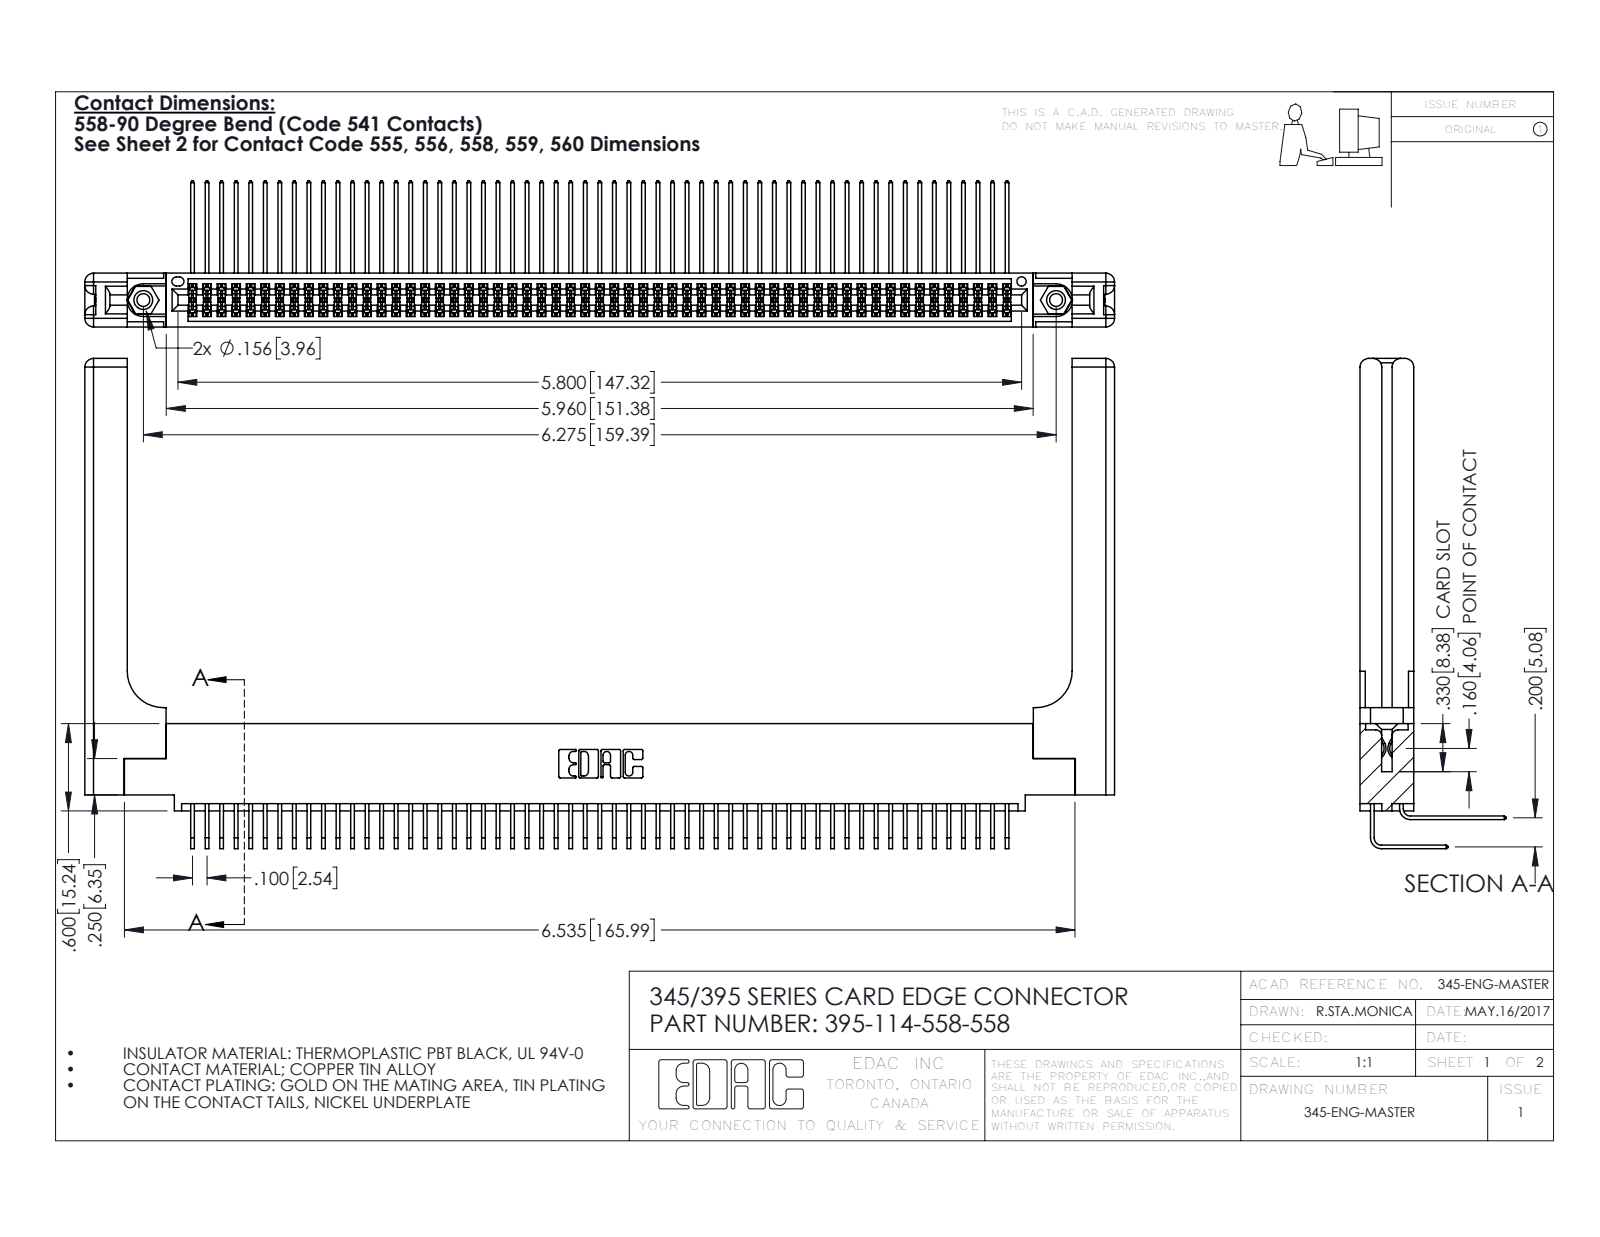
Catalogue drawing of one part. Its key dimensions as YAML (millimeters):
part_name: "345-292-001_558 559 Tail - 1; 345-292-001_558 Tail - 2; 345-220-058_345-220-058; 345 Part_0.110 Offset - 0.156 Dia-TH (+2 more)"
step_written_by: "SolidWorks 2016 (CONFIG_CONTROL_DESIGN)"
units: millimeters
bodies: {solids: 119, faces: 6314, planar: 4222, cylindrical: 2032, other: 60}
overall_size: [179.8, 85.6, 25.5]
volume: 26660
surface_area: 35430
round_holes:
  - {diameter: 2.3, count: 2}
  - {diameter: 3.2, count: 2}
  - {diameter: 4, count: 2}
  - {diameter: 1.6, count: 1}
round_bosses_or_shafts:
  - {diameter: 3.9, count: 2}
partial_cylinders:
  - {radius: 0.2, count: 172}
  - {radius: 0.3, count: 22}
  - {radius: 1.5, count: 16}
  - {radius: 0.2, count: 6}
  - {radius: 0.8, count: 6}
  - {radius: 0.7, count: 3}
  - {radius: 0.4, count: 2}
  - {radius: 0.5, count: 2}
face_to_face_distances: [1.8, 7.6, 9.4, 5.1, 2.5, 6.9, 0.6, 5.7, 3.8, 3.8]
hole_center_spacings: [6.9, 153.4, 159.4]
